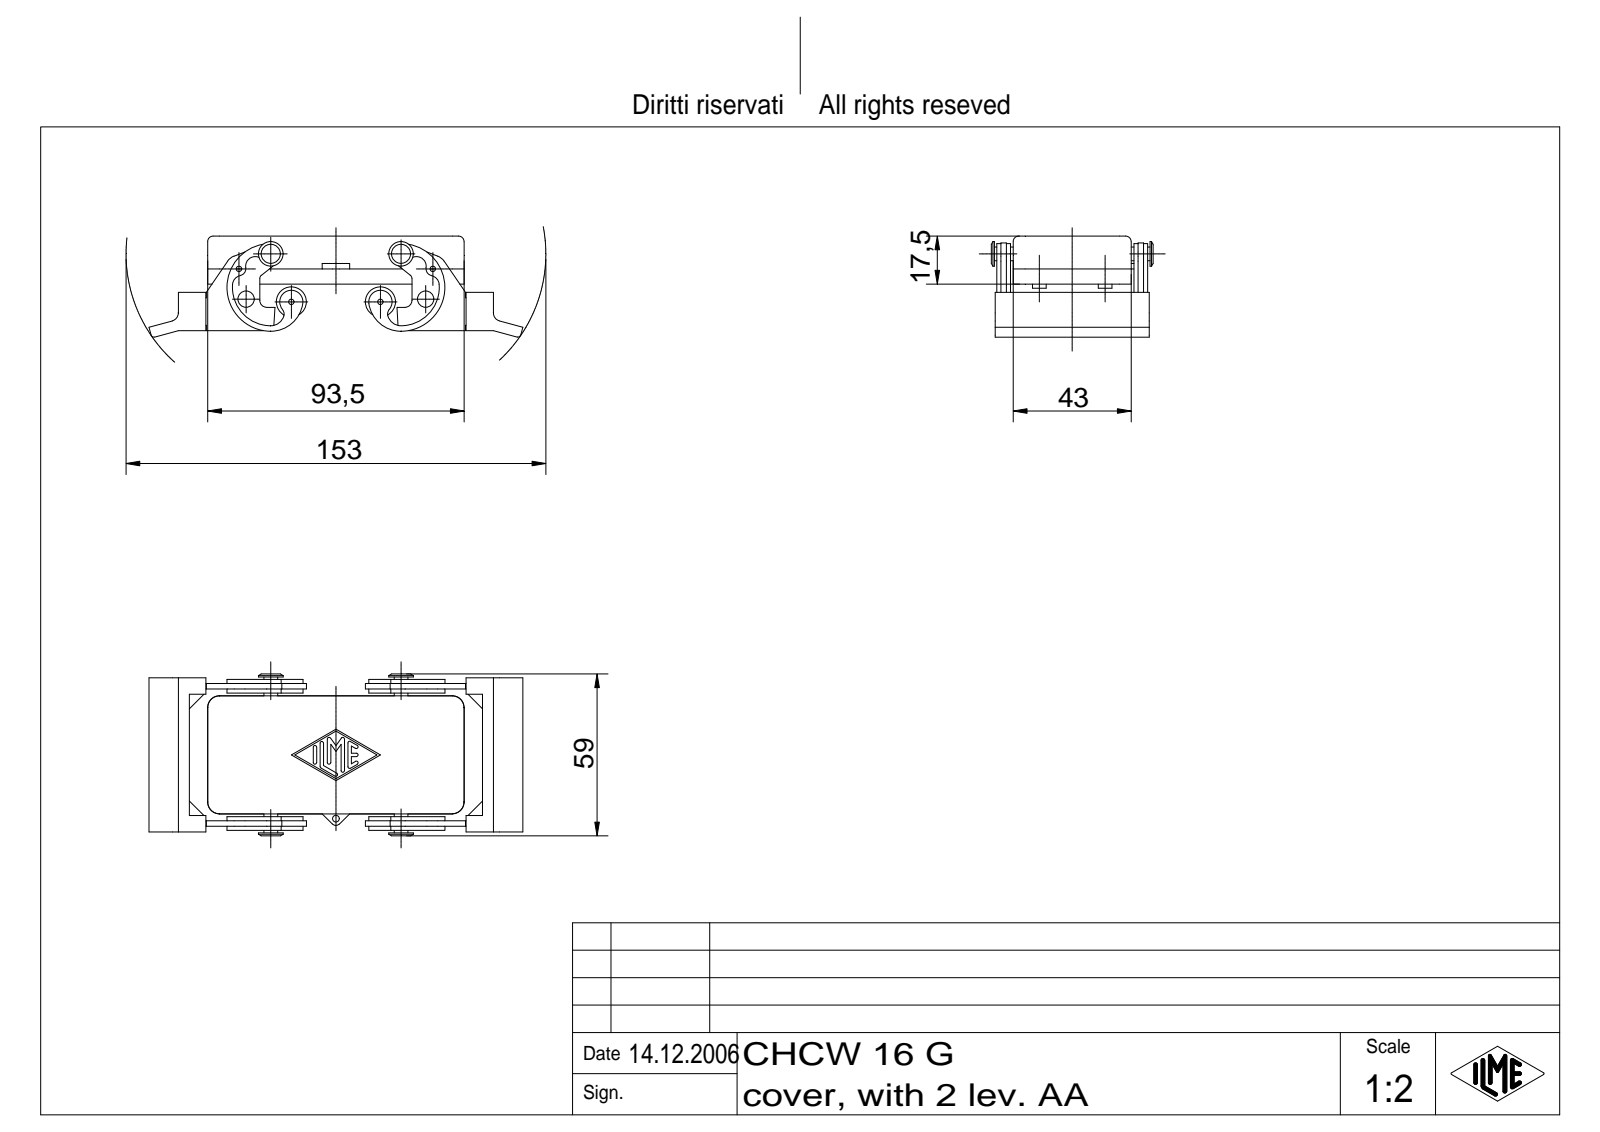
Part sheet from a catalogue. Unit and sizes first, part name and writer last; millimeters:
Units: millimetres
Overall size (bounding box): 136.34 × 59 × 36.87
Round holes (diameter × count): ⌀2 ×4, ⌀2.5 ×3, ⌀6 ×1
Round bosses / shafts (diameter × count): ⌀11 ×2, ⌀9 ×2, ⌀5 ×2
Partial cylindrical surfaces — rounded edges, fillets, slot ends (radius × count): R0.62 ×14, R2 ×12, R2.5 ×6, R4.3 ×6, R3.5 ×4, R5 ×4, R1 ×2, R1.5 ×2
Main face-to-face distances: 3, 4.5, 38.5, 43, 2.5, 7, 17.5, 50, 14.5, 4.49
Hole centre spacings: 22.56, 52.98, 11.3, 16.53, 32.5, 49.01, 68.98, 70.7
Volume: 50 973 mm³ · Surface area: 33 737 mm²
Bodies: 1 solid, 501 faces (165 planar, 153 cylindrical, 183 other)
Part name (STEP PRODUCT): CHCW 16 G
STEP written by: Autodesk Inventor 7 (AUTOMOTIVE_DESIGN)
